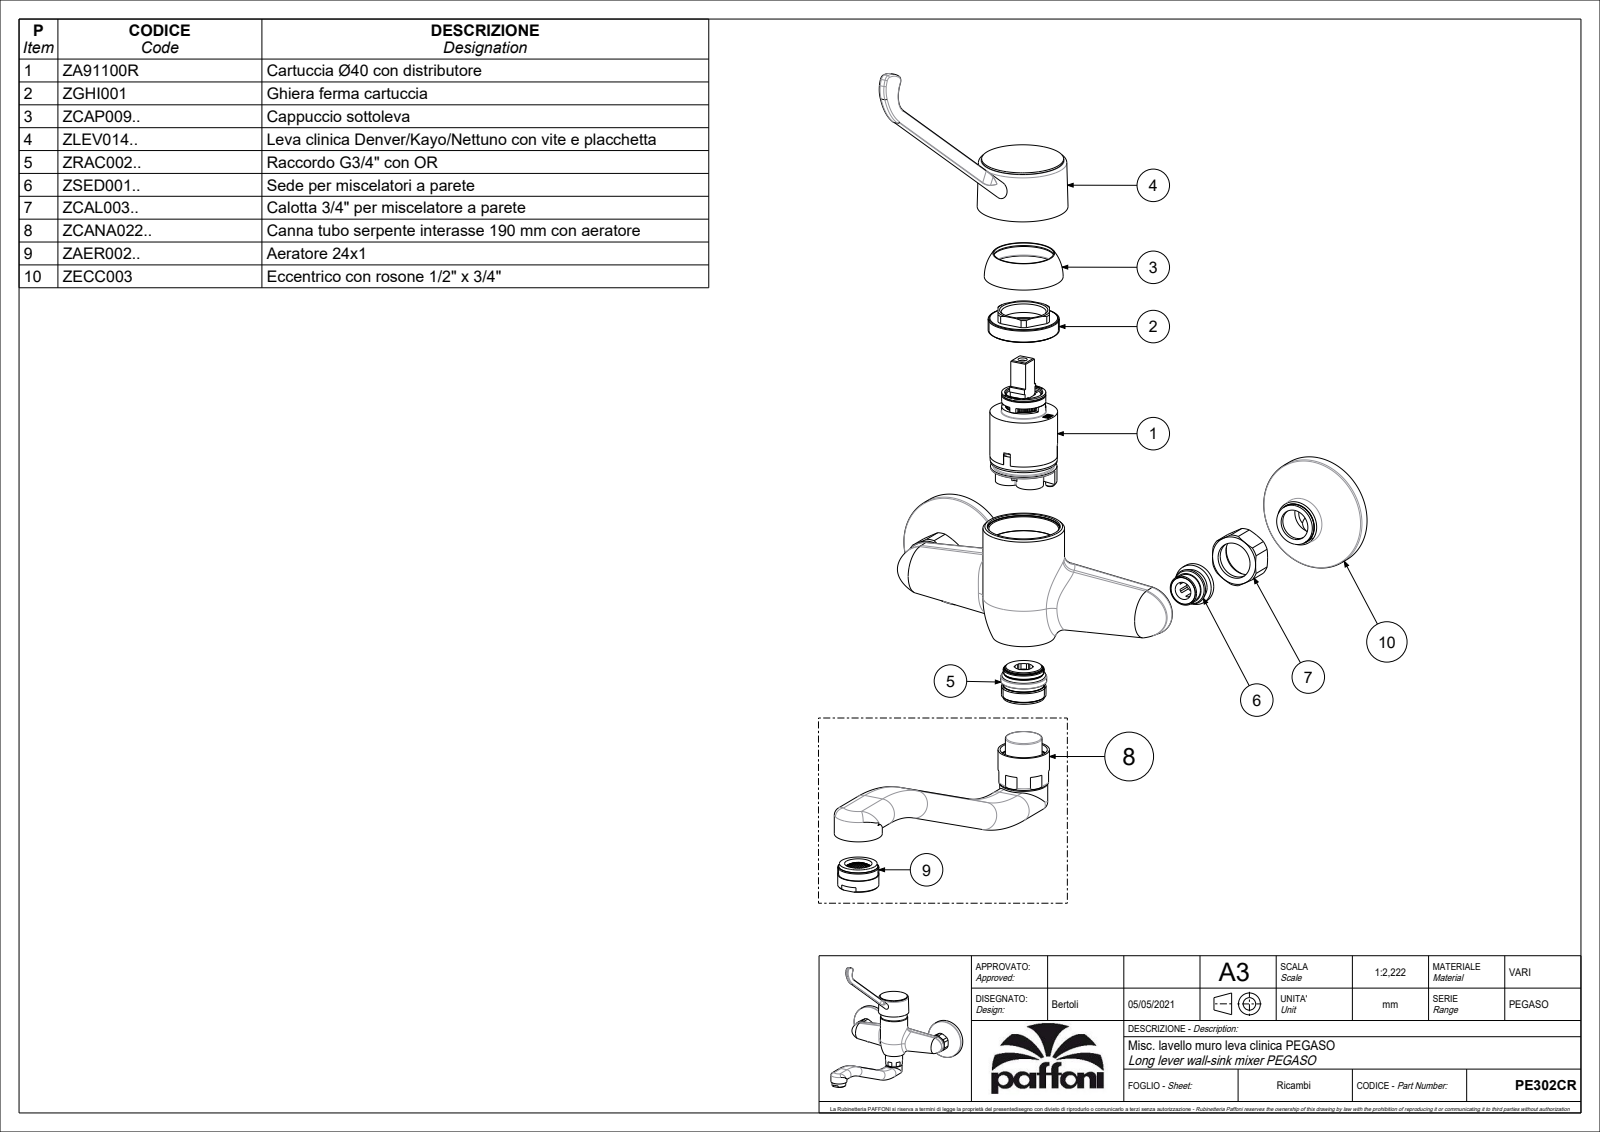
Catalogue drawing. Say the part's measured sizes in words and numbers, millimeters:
The part is named "PE302CR_SW0001". Its 3-D file was written by "CREO PARAMETRIC BY PTC INC, 2022124 (CONFIG_CONTROL_DESIGN)". It is 4 solids with 1268 faces: 972 planar, 107 cylindrical and 189 other. Overall it measures 281 by 246.88 by 216 millimeters. Its volume is 440 745 cubic millimeters and its surface area 99 897 square millimeters. Round holes: 2 of diameter 16, 2 of diameter 26.7, 1 of diameter 17, 1 of diameter 17.2, 1 of diameter 18.5, 1 of diameter 20, 1 of diameter 21, 1 of diameter 23.3, 1 of diameter 24.2, 1 of diameter 27, 1 of diameter 27.5. Round bosses or shafts: 2 of diameter 66, 2 of diameter 28, 2 of diameter 26.4, 2 of diameter 21, 1 of diameter 47.85, 1 of diameter 47.6, 1 of diameter 30, 1 of diameter 24. Partial cylindrical surfaces (rounded edges, fillets, slot ends): 6 of radius 7.2, 6 of radius 8, 4 of radius 0.3, 2 of radius 13, 2 of radius 15.5, 2 of radius 18.3, 2 of radius 25.63, 2 of radius 94. The main face-to-face distances are 0.8, 15.2, 4.5, 1.5, 29, 16, 14.4, 33, 34.5, 8.2. The hole center spacings are 150, 193.
